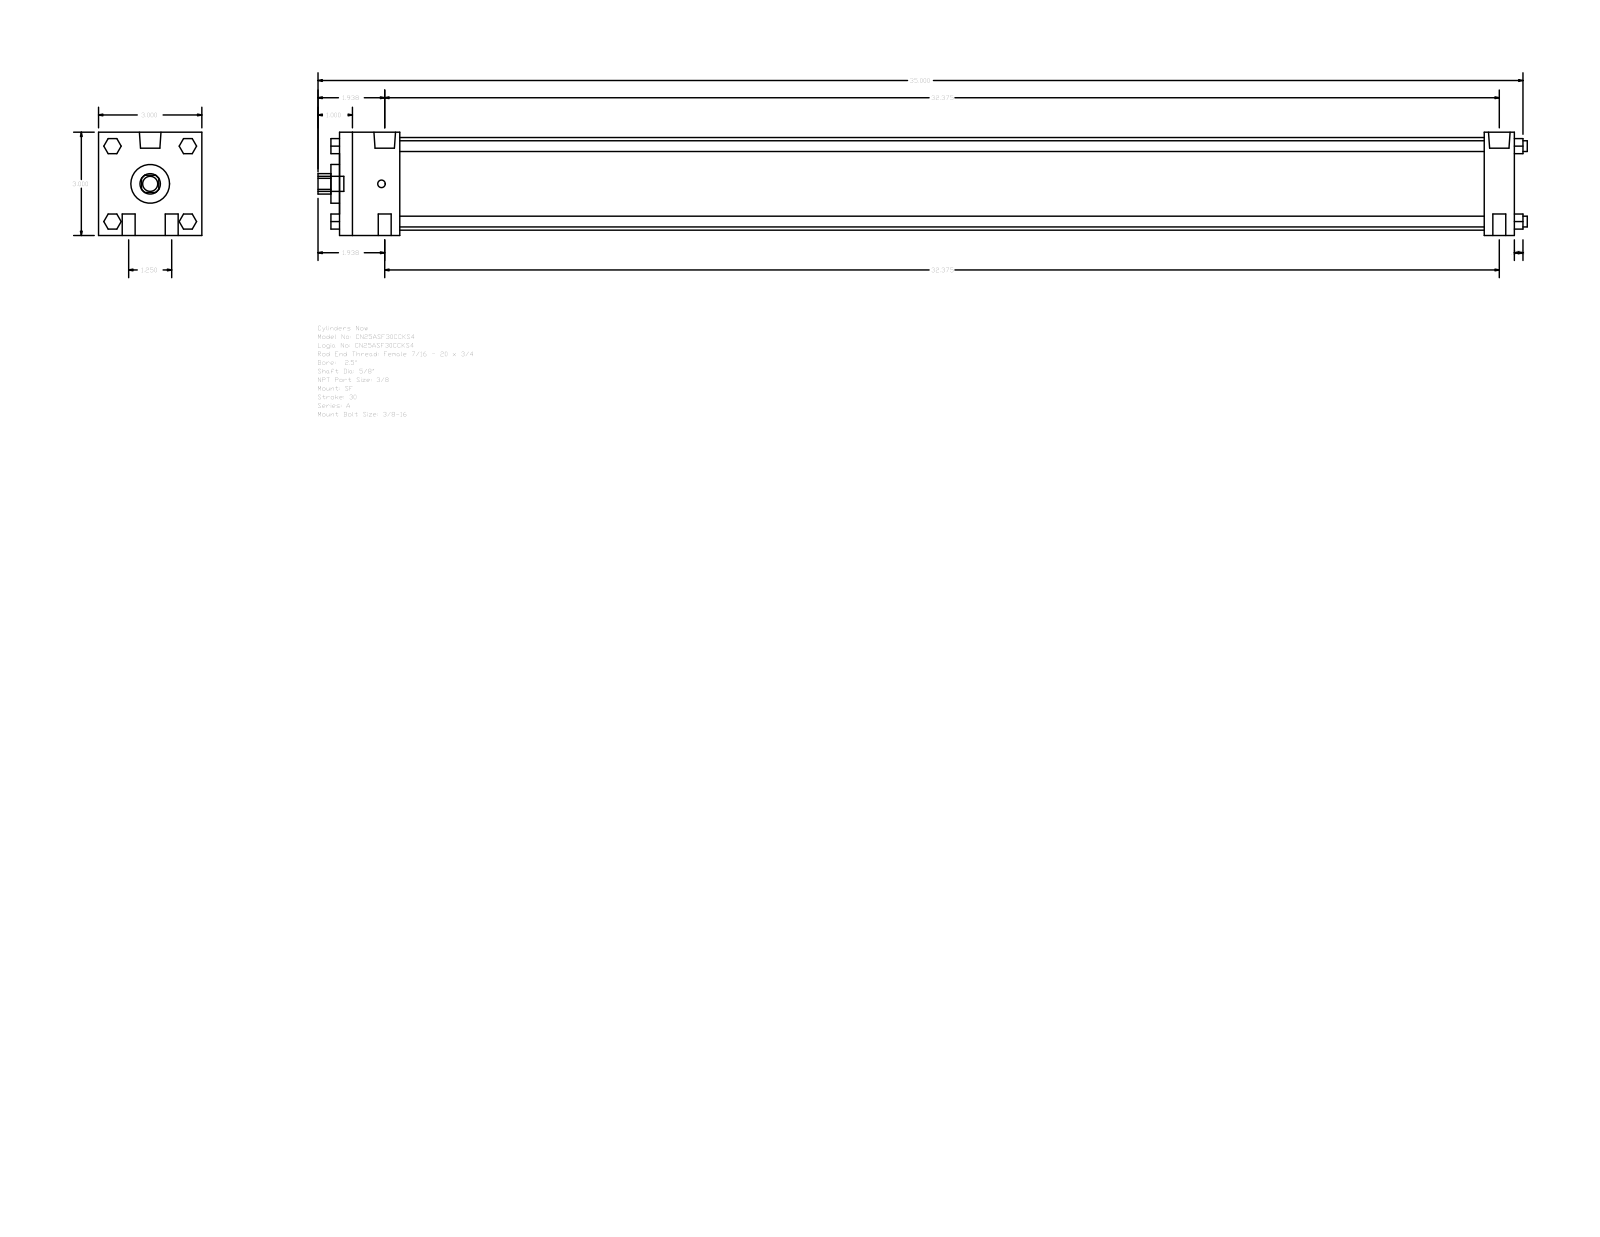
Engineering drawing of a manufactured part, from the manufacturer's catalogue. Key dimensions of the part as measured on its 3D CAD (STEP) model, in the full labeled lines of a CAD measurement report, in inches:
Part name (STEP PRODUCT): A_SF__0250_0.625
STEP written by: GSSL Pune (CONFIG_CONTROL_DESIGN)
Units: inches
Bodies: 0 solids, 124 faces (94 planar, 30 cylindrical, 0 other)
Overall size (bounding box): 35.125 × 3 × 3
Round holes (diameter × count): ⌀0.625 ×1, ⌀1.125 ×1, ⌀2.69 ×1
Round bosses / shafts (diameter × count): ⌀0.375 ×4, ⌀0.313 ×4, ⌀0.627 ×2, ⌀0.219 ×2, ⌀0.437 ×1
Partial cylindrical surfaces — rounded edges, fillets, slot ends (radius × count): R0.297 ×1
Main face-to-face distances: 3, 34.125, 1.75, 33.25, 0.875, 31.5, 32.375, 34.375, 0.25, 2
